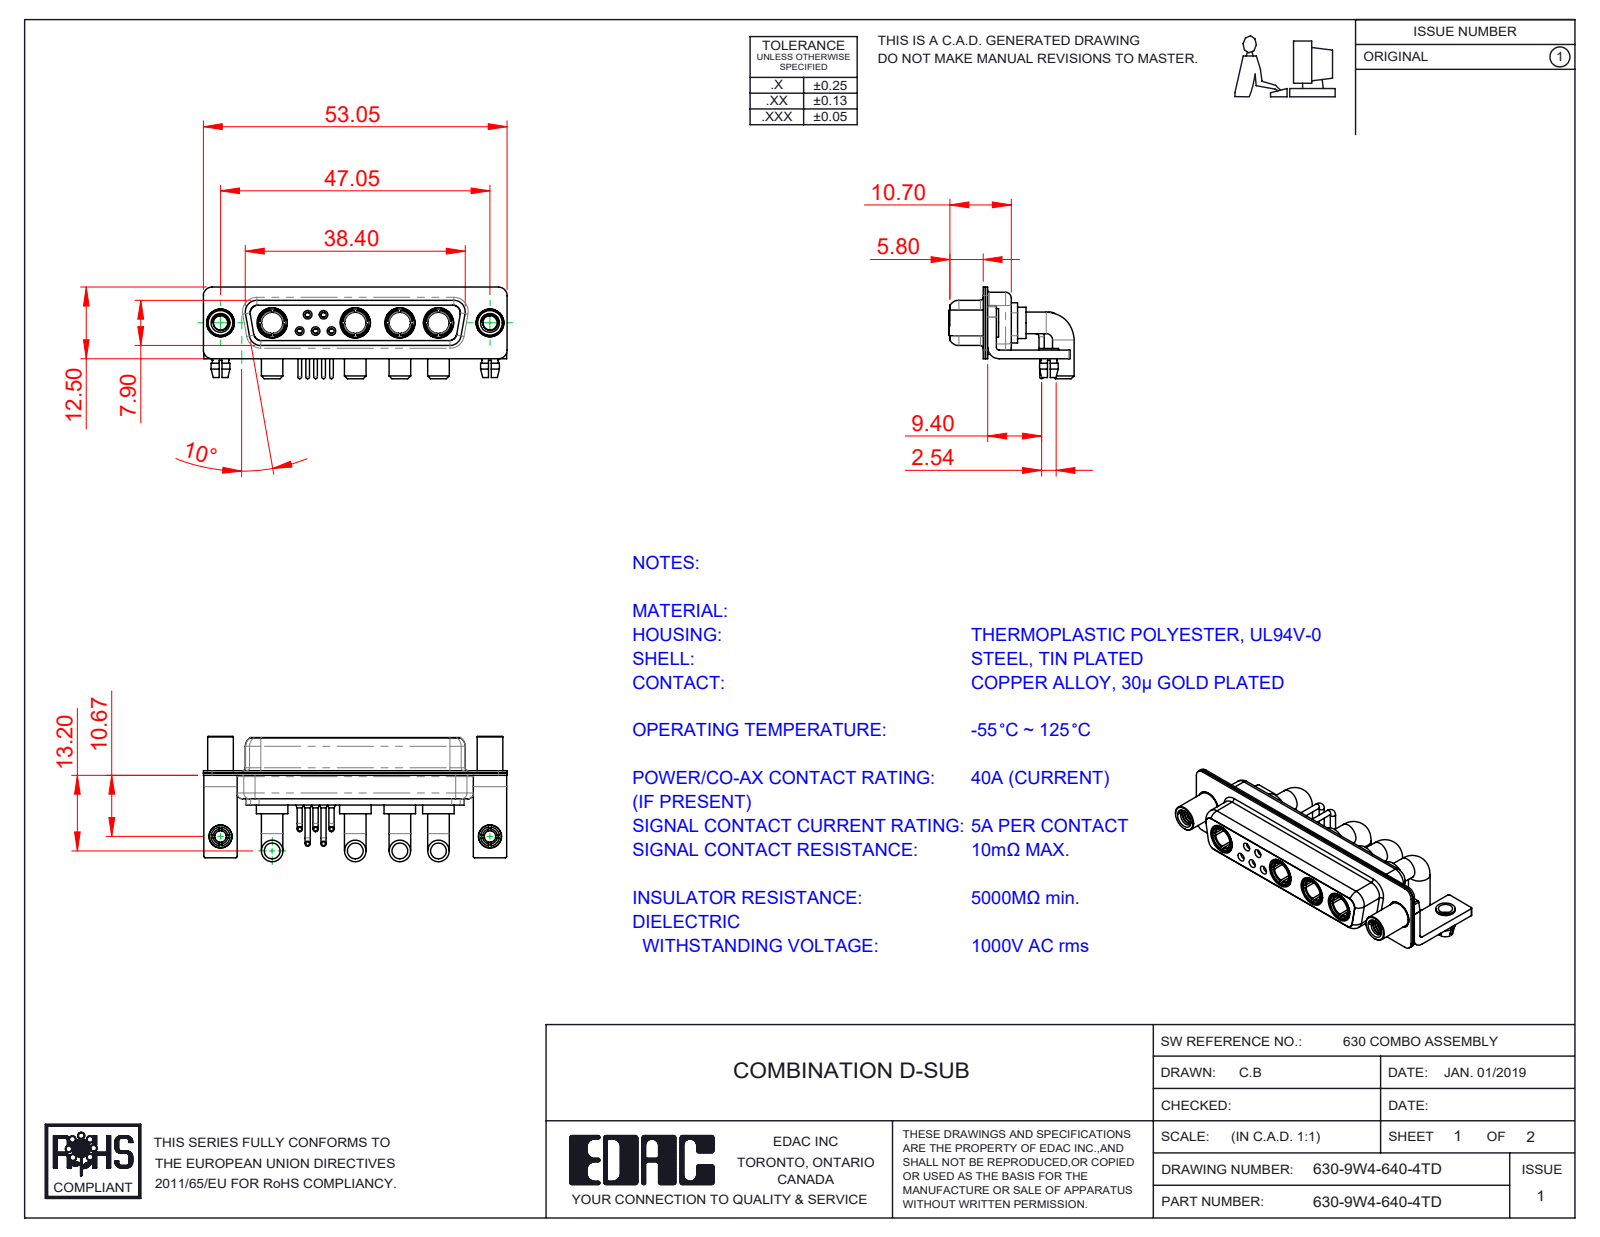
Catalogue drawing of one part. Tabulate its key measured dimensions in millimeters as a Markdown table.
| quantity | value |
| --- | --- |
| part name | Power Socket_40A RA; 630Combo Threaded Standoff_D; 630-9W4-640-4TD; 630Combo Shell Rear_25 Contacts (+6 more) |
| STEP written by | SolidWorks 2020 (CONFIG_CONTROL_DESIGN) |
| units | millimeters |
| bodies | 22 solids, 1046 faces (328 planar, 456 cylindrical, 262 other) |
| overall size | 53.05 × 21.88 × 16 |
| volume | 4 734 mm³ |
| surface area | 10 155 mm² |
| round holes (diameter × count) | 2 × 7, 4.85 × 6, 0.9 × 5, 1.1 × 5, 1.5 × 5, 2.5 × 4, 3.7 × 4, 5.3 × 4, 1.6 × 3, 1.7 × 2, 3.2 × 2, 4 × 2 |
| round bosses / shafts (diameter × count) | 3.75 × 8, 0.9 × 5, 0.65 × 5, 5.5 × 4, 5.2 × 4, 4.96 × 4, 4.75 × 4, 5 × 2 |
| partial cylindrical surfaces (radius × count) | 0.25 × 16, 1.5 × 16, 2 × 13, 1.35 × 8, 1.6 × 8, 0.5 × 5, 0.6 × 4, 0.65 × 4 |
| main face-to-face distances | 0.4, 0.45, 1.4, 8.45, 1.8, 0.8, 8.9, 6.2, 7.05, 1.5 |
| hole center spacings | 3.16, 2.77, 47.05, 4.4, 5.02, 5.03, 5.04, 5.54 |
